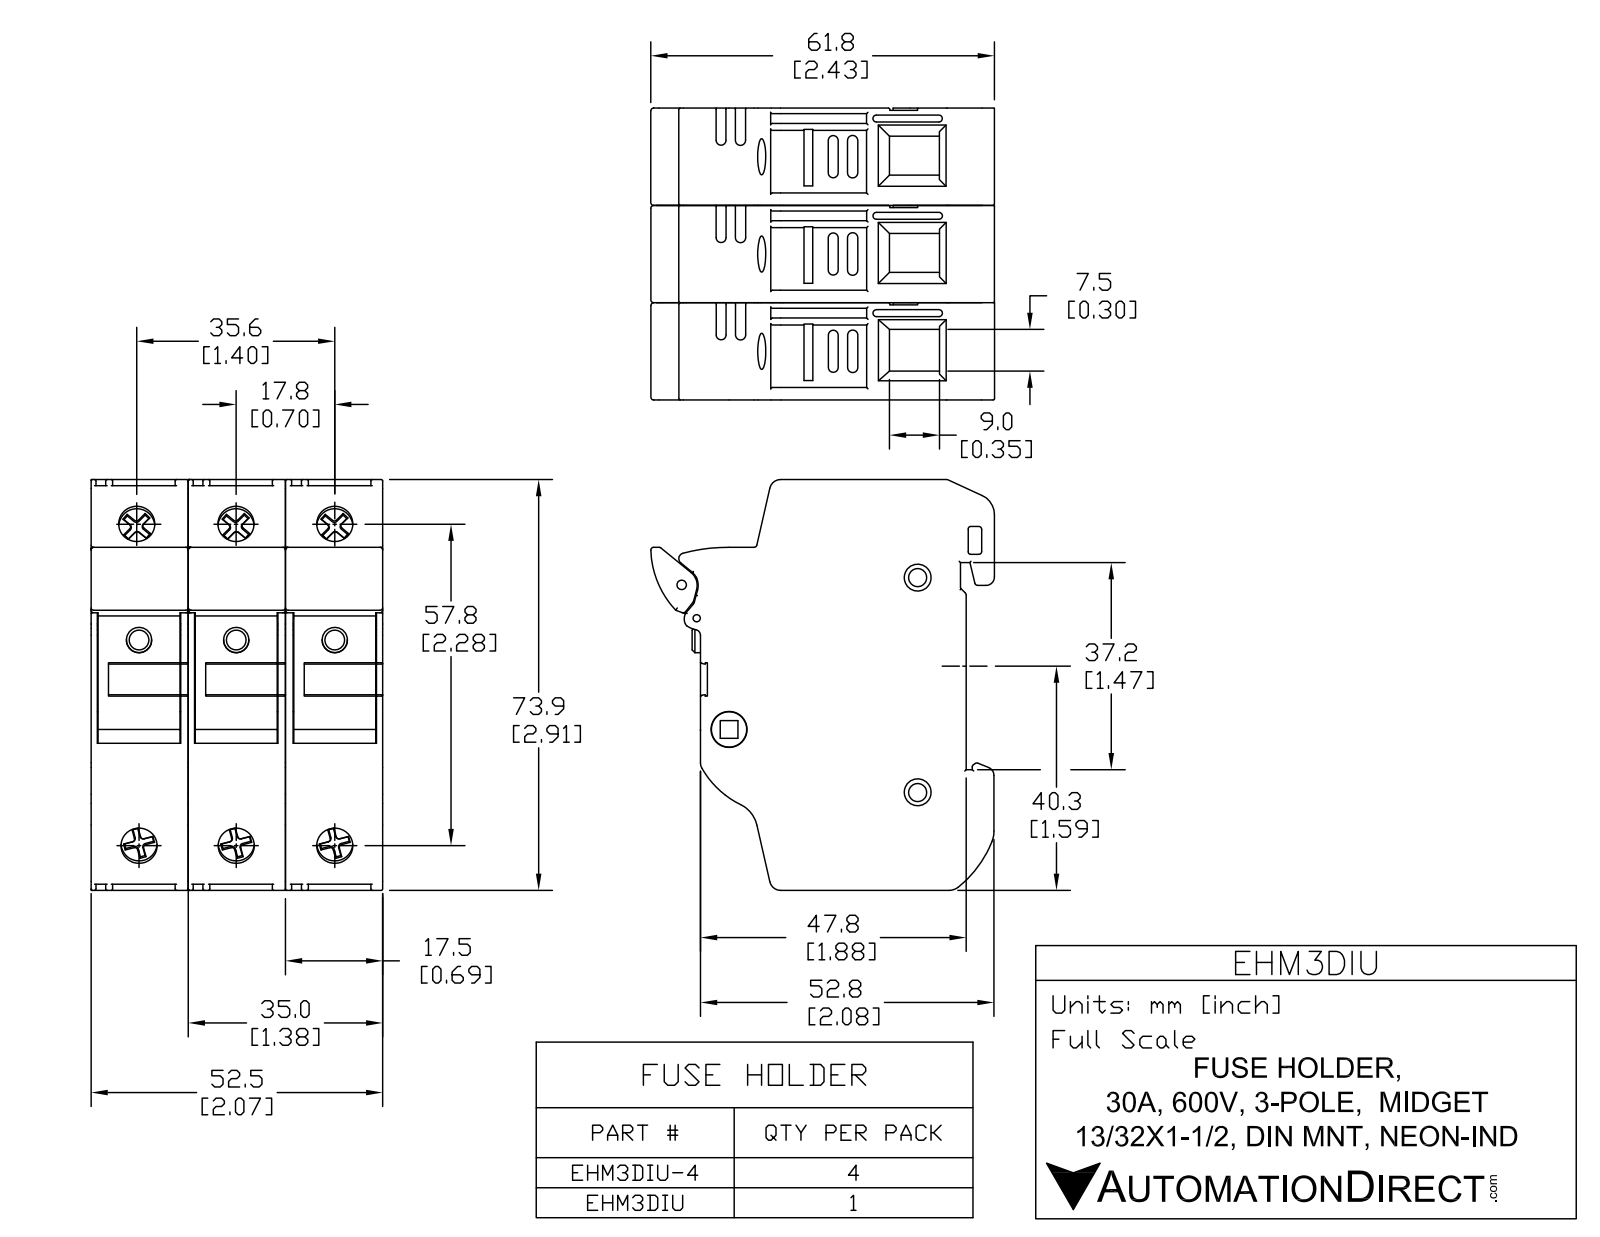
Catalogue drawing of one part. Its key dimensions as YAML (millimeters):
part_name: "EHM3DIU"
step_written_by: "SolidWorks 2011 (AUTOMOTIVE_DESIGN)"
units: millimeters
bodies: {solids: 2, faces: 1598, planar: 751, cylindrical: 525, other: 322}
overall_size: [73.88, 61.82, 52.52]
volume: 158271
surface_area: 48401
round_holes:
  - {diameter: 6.5, count: 6}
  - {diameter: 3.25, count: 2}
  - {diameter: 4.83, count: 2}
  - {diameter: 1.3, count: 1}
  - {diameter: 1.7, count: 1}
  - {diameter: 6.48, count: 1}
round_bosses_or_shafts:
  - {diameter: 4.55, count: 3}
  - {diameter: 6.35, count: 1}
partial_cylinders:
  - {radius: 0.25, count: 84}
  - {radius: 0.2, count: 57}
  - {radius: 0.62, count: 12}
  - {radius: 0.5, count: 11}
  - {radius: 2, count: 10}
  - {radius: 0.51, count: 9}
  - {radius: 0.89, count: 9}
  - {radius: 0.92, count: 9}
face_to_face_distances: [17.5, 35, 52.5, 1.25, 1.58, 16.25, 27.51, 29.09, 22.94, 24.71]
hole_center_spacings: [17.51, 35.02, 6.58, 20.83, 27.36, 35.77, 35.79, 38.61]
